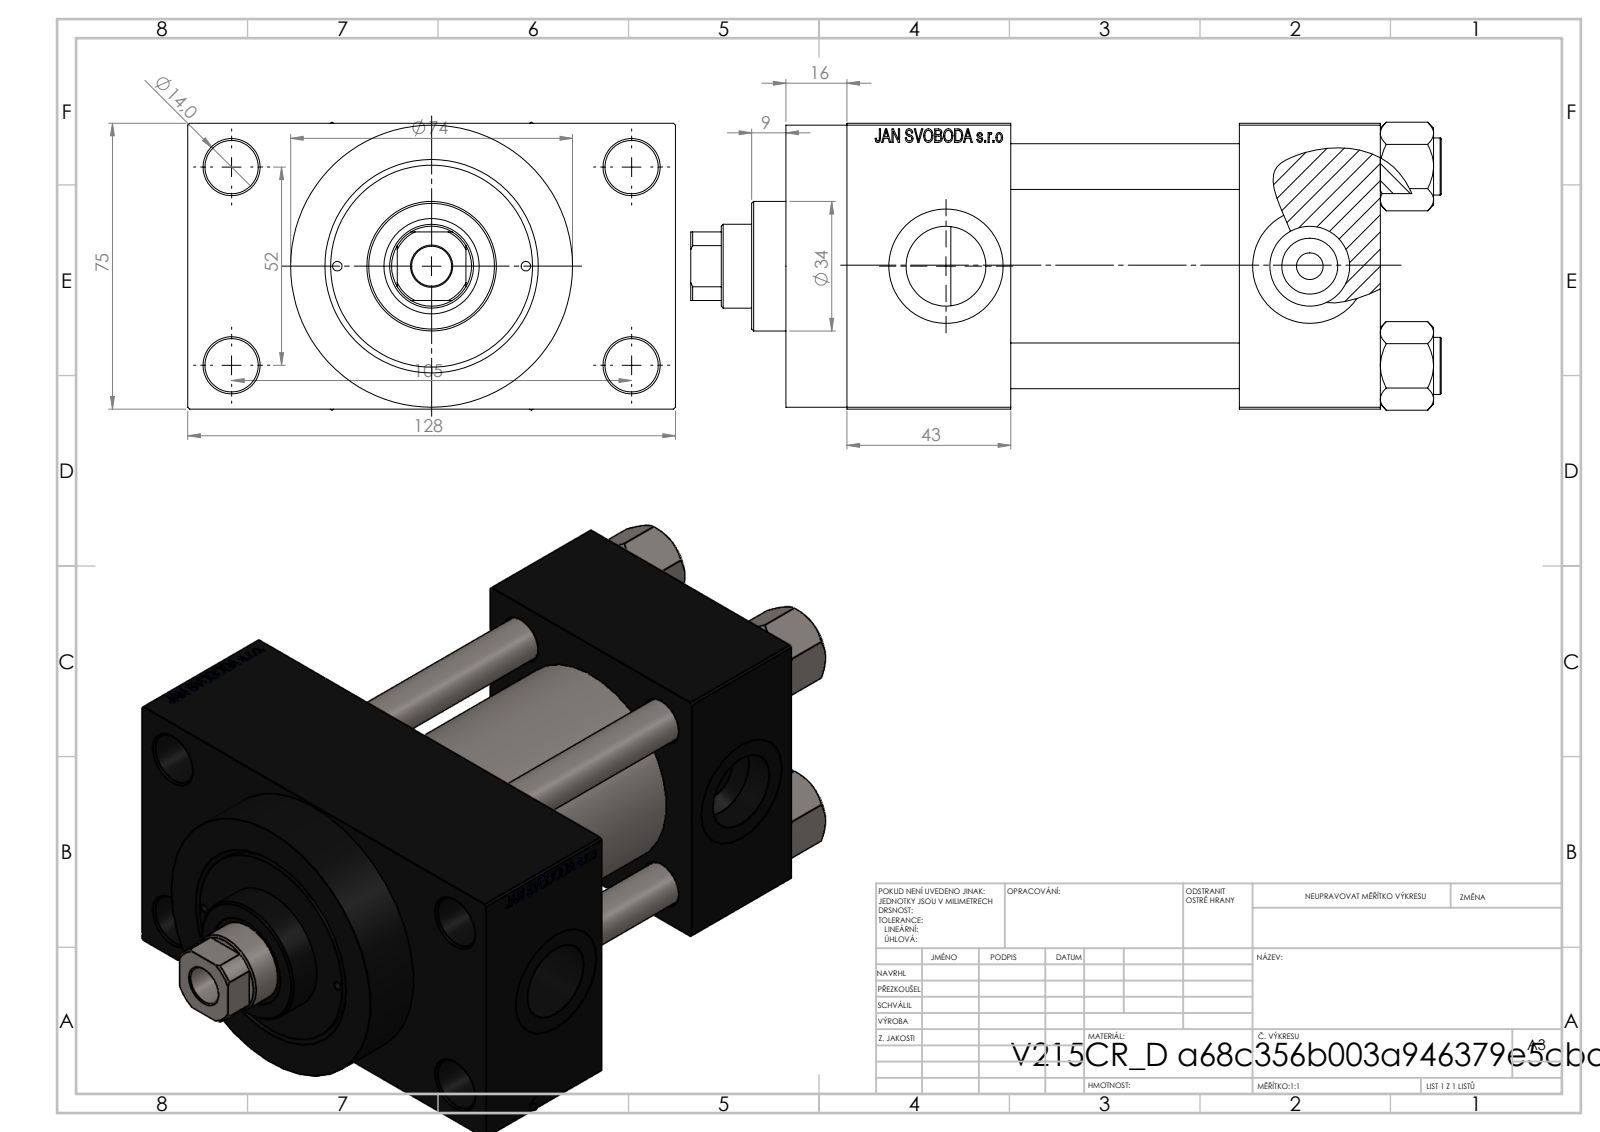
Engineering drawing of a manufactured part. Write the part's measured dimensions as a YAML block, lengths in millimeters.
part_name: "V215CR_D_TYCINKA; NUT_M5_D; V215CR_VCP_D; V215_VC_A (+1 more)"
step_written_by: "SolidWorks 2019 (CONFIG_CONTROL_DESIGN)"
units: millimeters
bodies: {solids: 11, faces: 1111, planar: 499, cylindrical: 92, other: 520}
overall_size: [197, 128, 75.54]
volume: 800314
surface_area: 167618
round_holes:
  - {diameter: 12, count: 4}
  - {diameter: 14, count: 4}
  - {diameter: 2.5, count: 2}
  - {diameter: 7, count: 2}
  - {diameter: 20.96, count: 2}
  - {diameter: 30, count: 2}
  - {diameter: 10.5, count: 1}
  - {diameter: 22, count: 1}
  - {diameter: 25, count: 1}
  - {diameter: 41, count: 1}
  - {diameter: 50, count: 1}
  - {diameter: 53, count: 1}
round_bosses_or_shafts:
  - {diameter: 15, count: 4}
  - {diameter: 74, count: 1}
  - {diameter: 56, count: 1}
  - {diameter: 34, count: 1}
partial_cylinders:
  - {radius: 10.5, count: 1}
face_to_face_distances: [75, 60, 37, 97, 26.5, 140, 103, 43, 101.5, 16]
hole_center_spacings: [26.19, 26.35, 36.98, 38.03, 52.3, 57.22, 58.43, 58.59]
